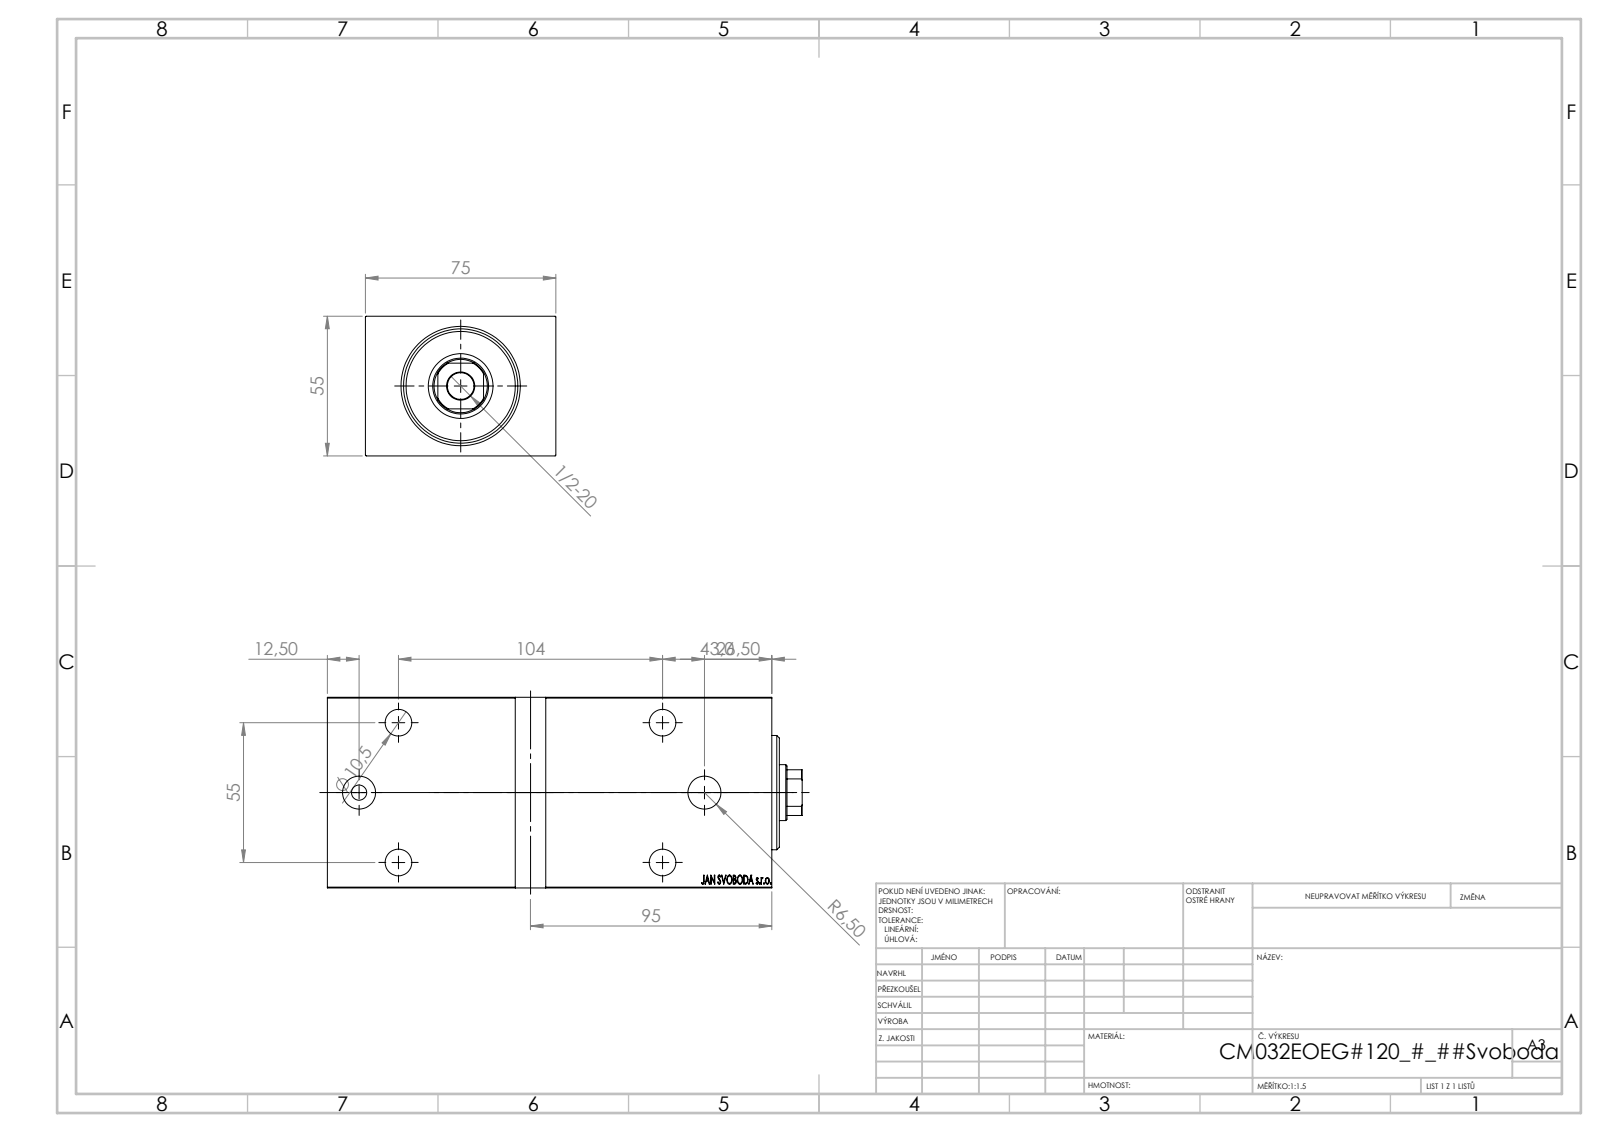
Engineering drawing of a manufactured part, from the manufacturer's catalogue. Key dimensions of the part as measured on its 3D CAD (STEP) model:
Part name (STEP PRODUCT): V450CM_E_VCP; V450CM_VC_B; V450CM_E_Body
STEP written by: SolidWorks 2019 (CONFIG_CONTROL_DESIGN)
Units: millimetres
Bodies: 3 solids, 846 faces (408 planar, 44 cylindrical, 394 other)
Overall size (bounding box): 187 × 75 × 55
Volume: 649 773 mm³ · Surface area: 100 203 mm²
Round holes (diameter × count): ⌀10.5 ×5, ⌀16.5 ×4, ⌀13 ×2, ⌀22 ×1, ⌀25.5 ×1, ⌀32 ×1, ⌀45 ×1
Round bosses / shafts (diameter × count): ⌀34 ×1, ⌀6 ×1
Partial cylindrical surfaces — rounded edges, fillets, slot ends (radius × count): R10.5 ×1
Main face-to-face distances: 55, 75, 175, 3, 10, 165, 5, 170, 160, 178
Hole centre spacings: 31.57, 32.07, 55, 104, 117.65, 122.62, 123.6, 136
